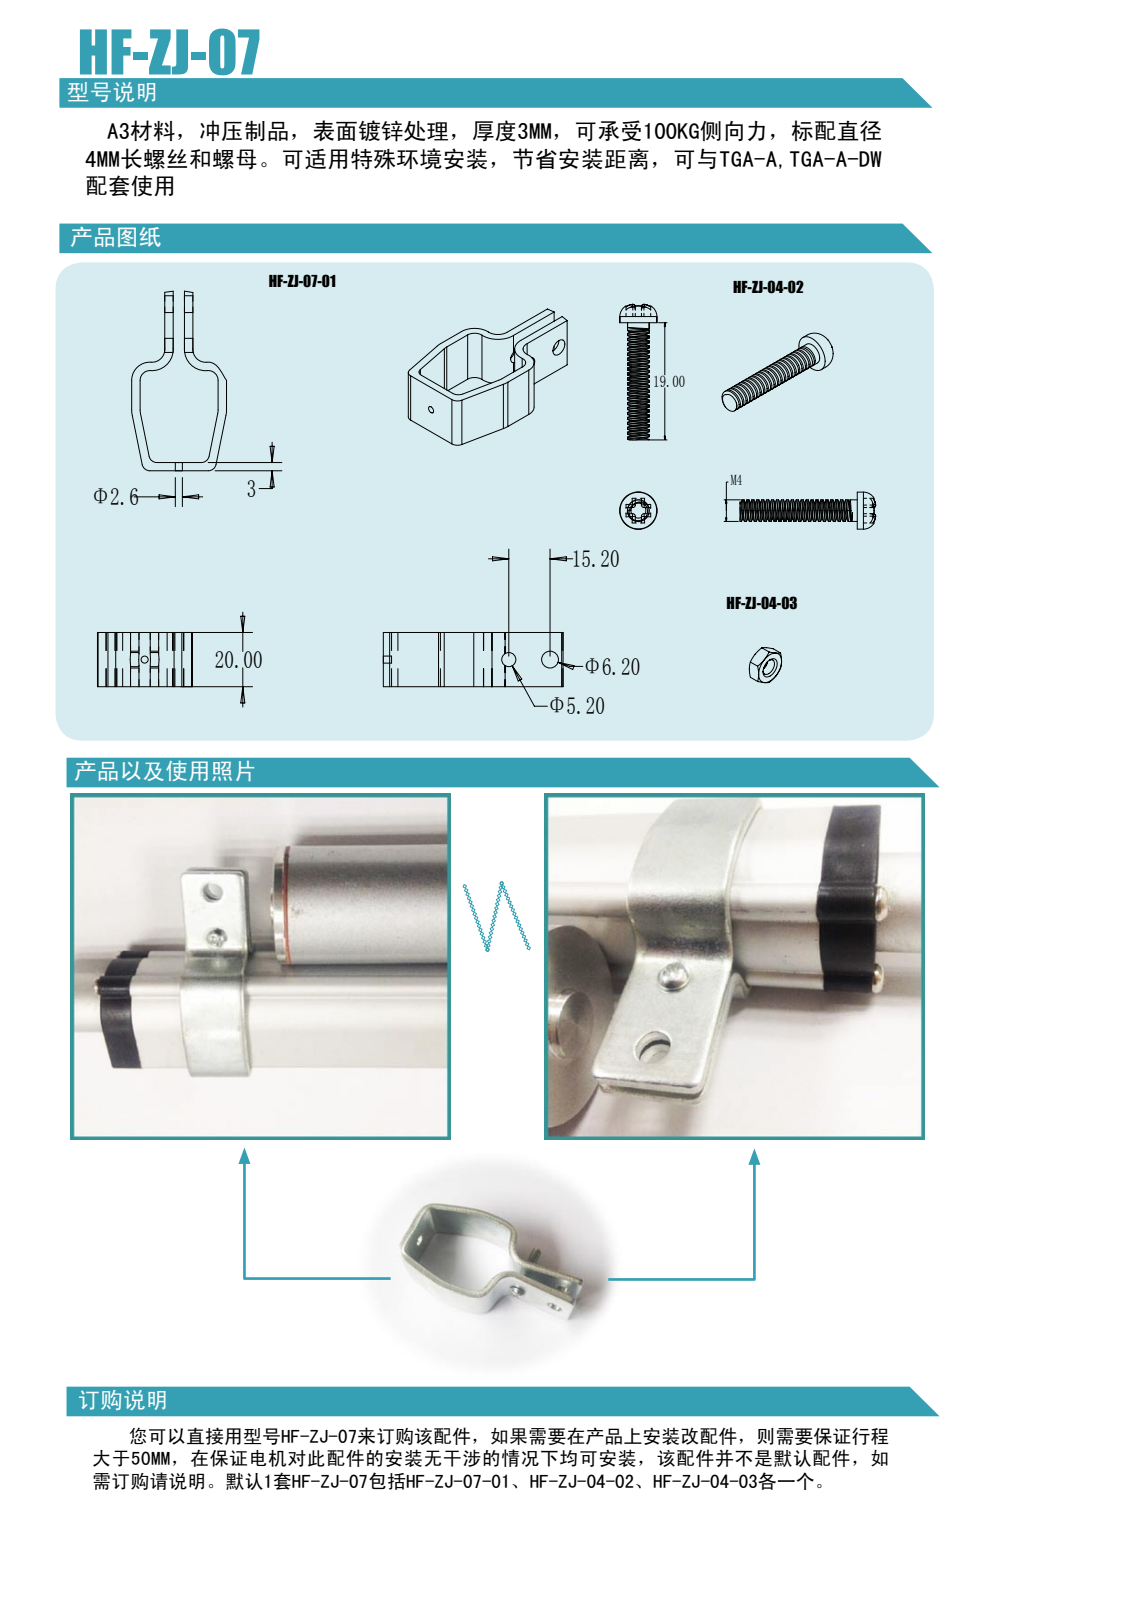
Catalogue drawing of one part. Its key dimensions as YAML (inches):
part_name: "ZJ-07"
step_written_by: "PRO/ENGINEER BY PARAMETRIC TECHNOLOGY CORPORATION, 2008380 (CONFIG_CONTROL_DESIGN)"
units: inches
bodies: {solids: 1, faces: 44, planar: 18, cylindrical: 26, other: 0}
overall_size: [66.239, 34.947, 20]
volume: 10089
surface_area: 7871
round_holes:
  - {diameter: 2.6, count: 1}
  - {diameter: 5.2, count: 1}
  - {diameter: 6.2, count: 1}
partial_cylinders:
  - {radius: 2.918, count: 4}
  - {radius: 3.609, count: 2}
  - {radius: 4.712, count: 2}
  - {radius: 6.43, count: 2}
  - {radius: 6.716, count: 2}
  - {radius: 7.819, count: 2}
  - {radius: 9.537, count: 2}
face_to_face_distances: [20, 4.152, 3.103, 7.254, 10.364, 7.261, 3.109, 3.037, 3.1, 3.115]
hole_center_spacings: [15.2]
